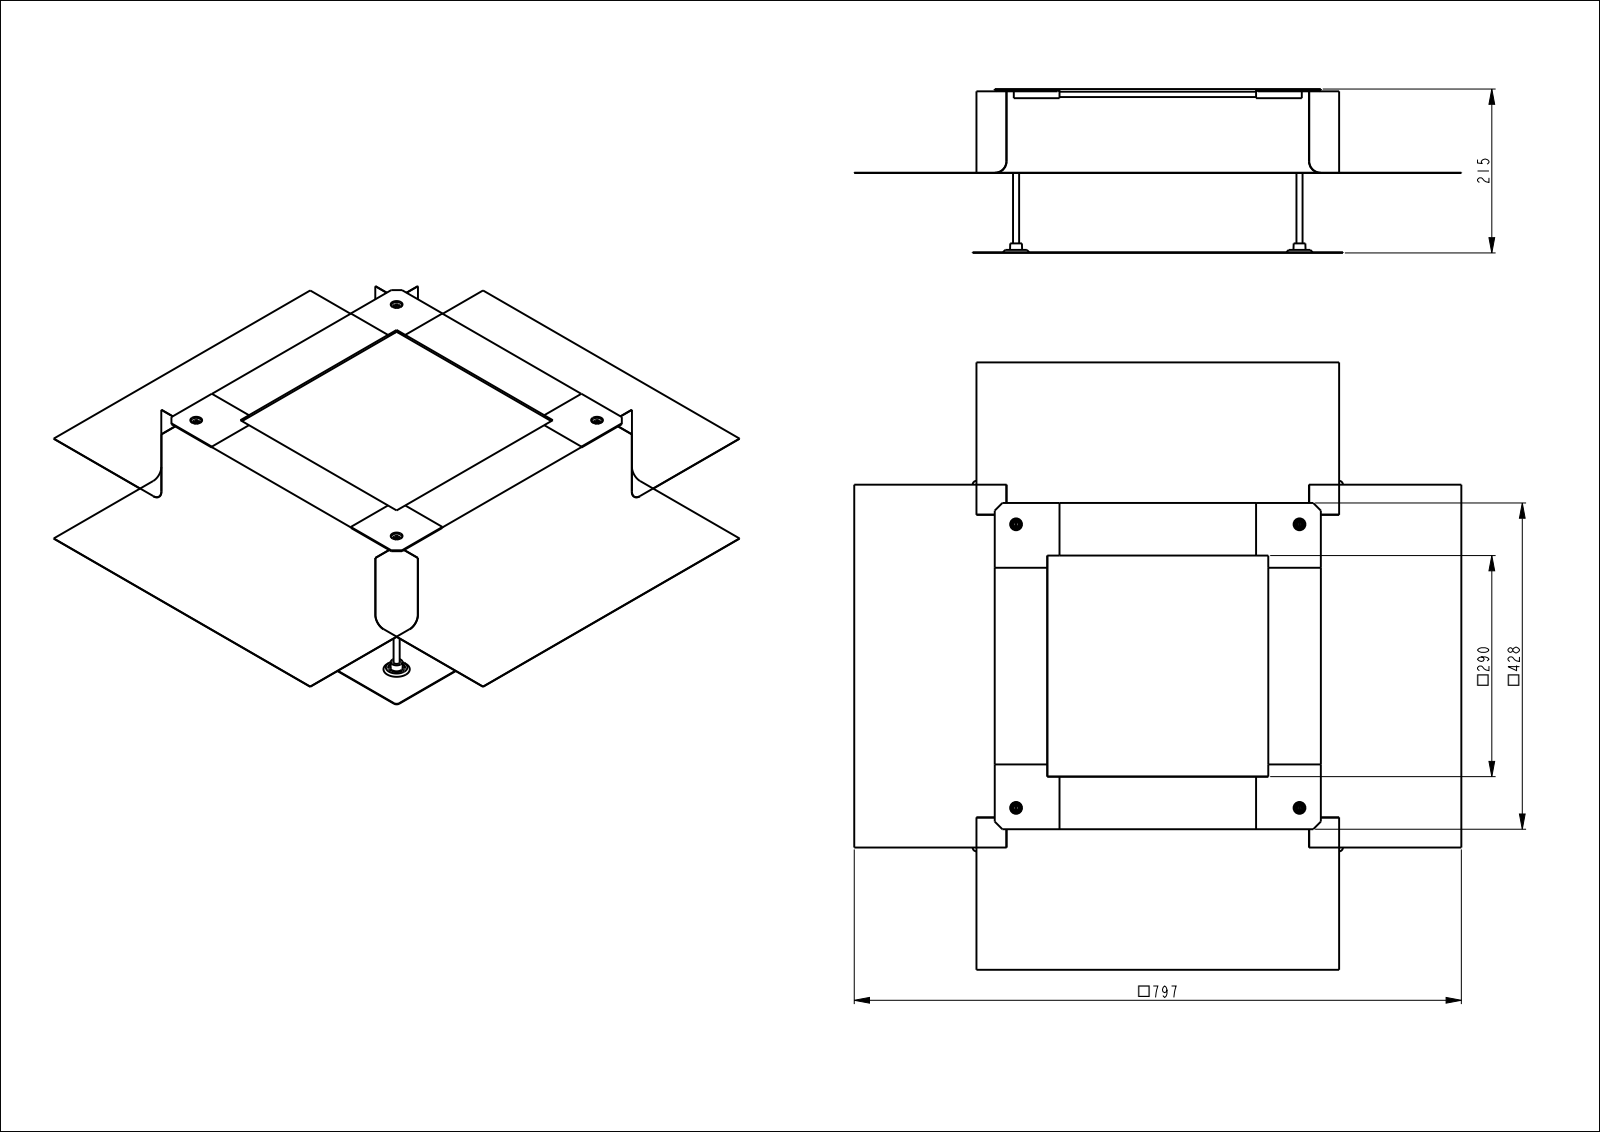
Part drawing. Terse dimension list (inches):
name: U05359KUN; U05349KUN; U09125KUN; U05365KUN (+5 more)
written by: CREO PARAMETRIC BY PTC INC, 2020281 (CONFIG_CONTROL_DESIGN)
unit: in
bodies: 22 solids, 2272 faces (1668 planar, 76 cylindrical, 528 other)
size: 31.37 × 31.37 × 8.465
volume: 69.14 in³; area: 3 337 in²
holes: 4× ⌀0.26, 4× ⌀0.335, 4× ⌀0.453, 4× ⌀0.65
bosses: 4× ⌀0.787, 4× ⌀0.315
rounds: 8× R0.02, 4× R0.197, 4× R0.591, 4× R0.606
face distances: 0.016, 0.035, 4.108, 4.128, 4.144, 4.093, 15.638, 0.157, 0.118, 8.307
hole spacings: 14.646, 20.712
